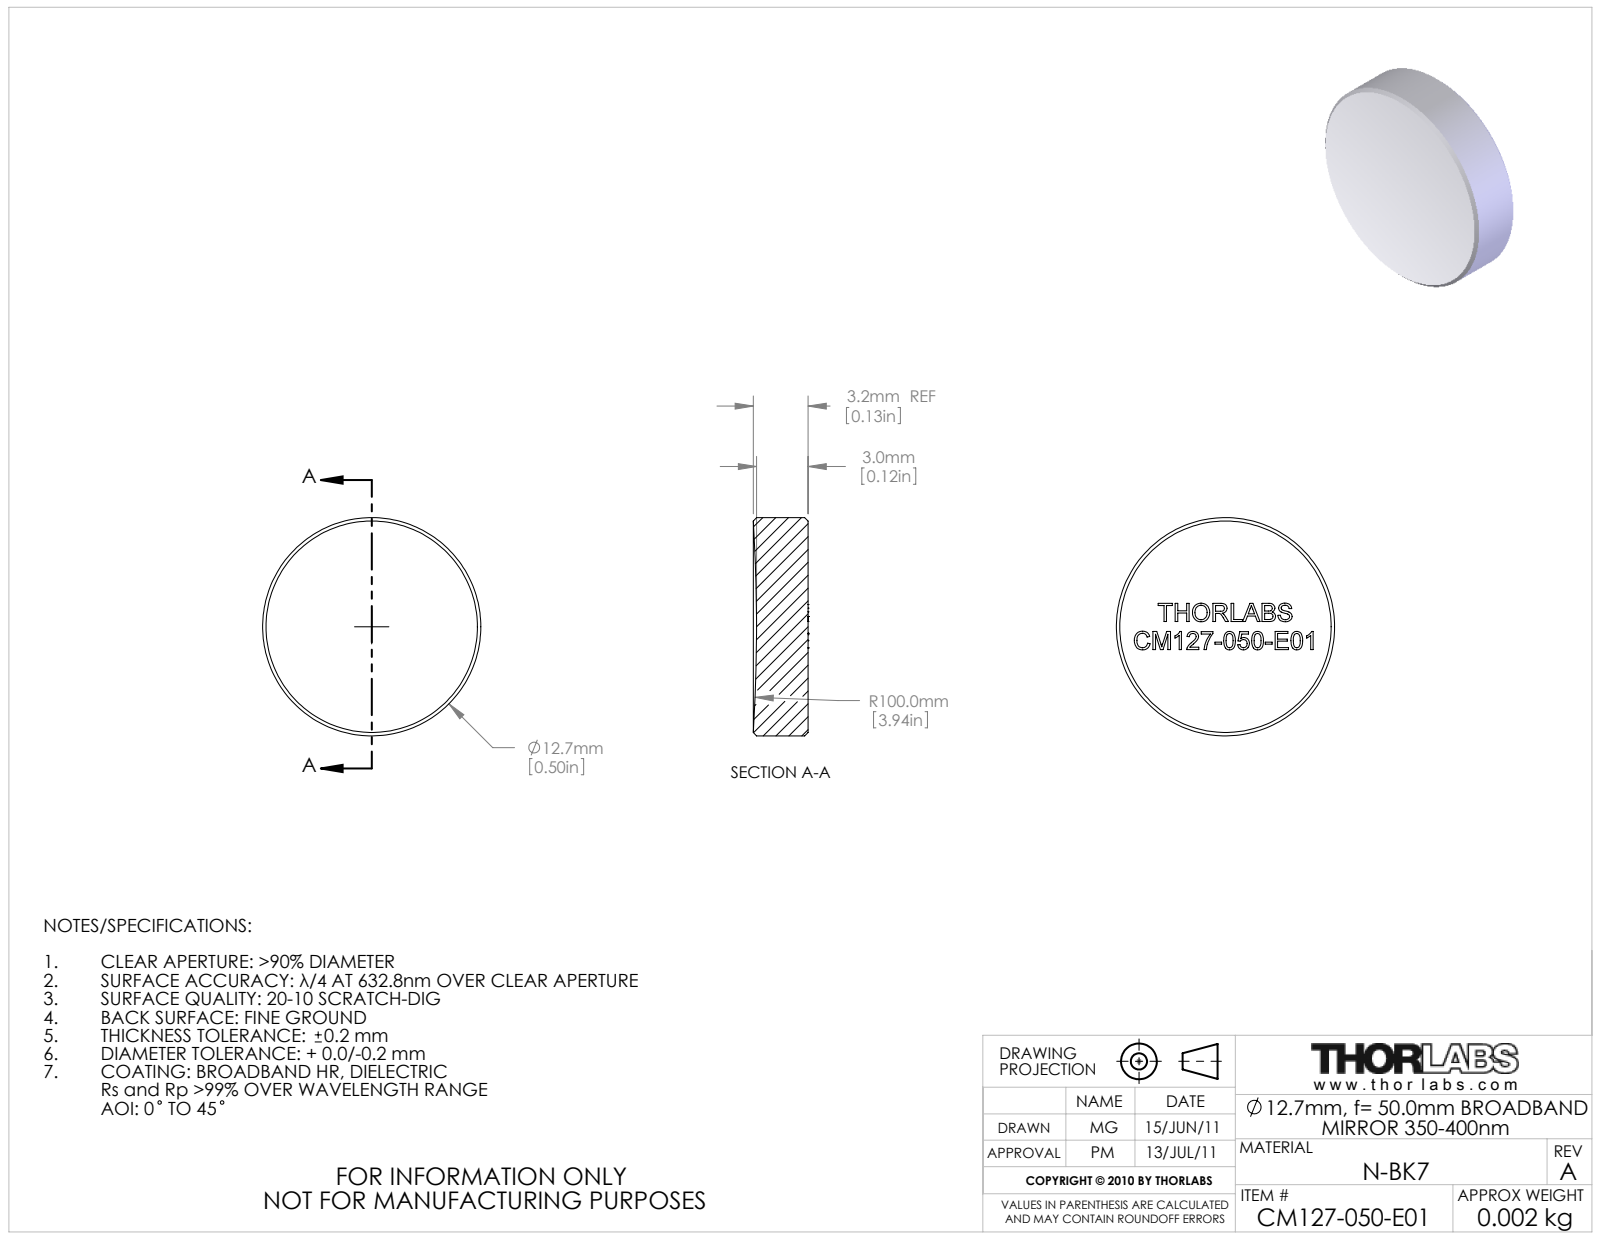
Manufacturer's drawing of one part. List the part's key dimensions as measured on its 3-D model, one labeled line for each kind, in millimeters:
Part name (STEP PRODUCT): 22610-E0W
STEP written by: SolidWorks 2011 (AUTOMOTIVE_DESIGN)
Units: millimetres
Bodies: 0 solids, 42 faces (31 planar, 2 cylindrical, 9 other)
Overall size (bounding box): 12.7 × 12.7 × 3.19
Round bosses / shafts (diameter × count): ⌀12.7 ×1
